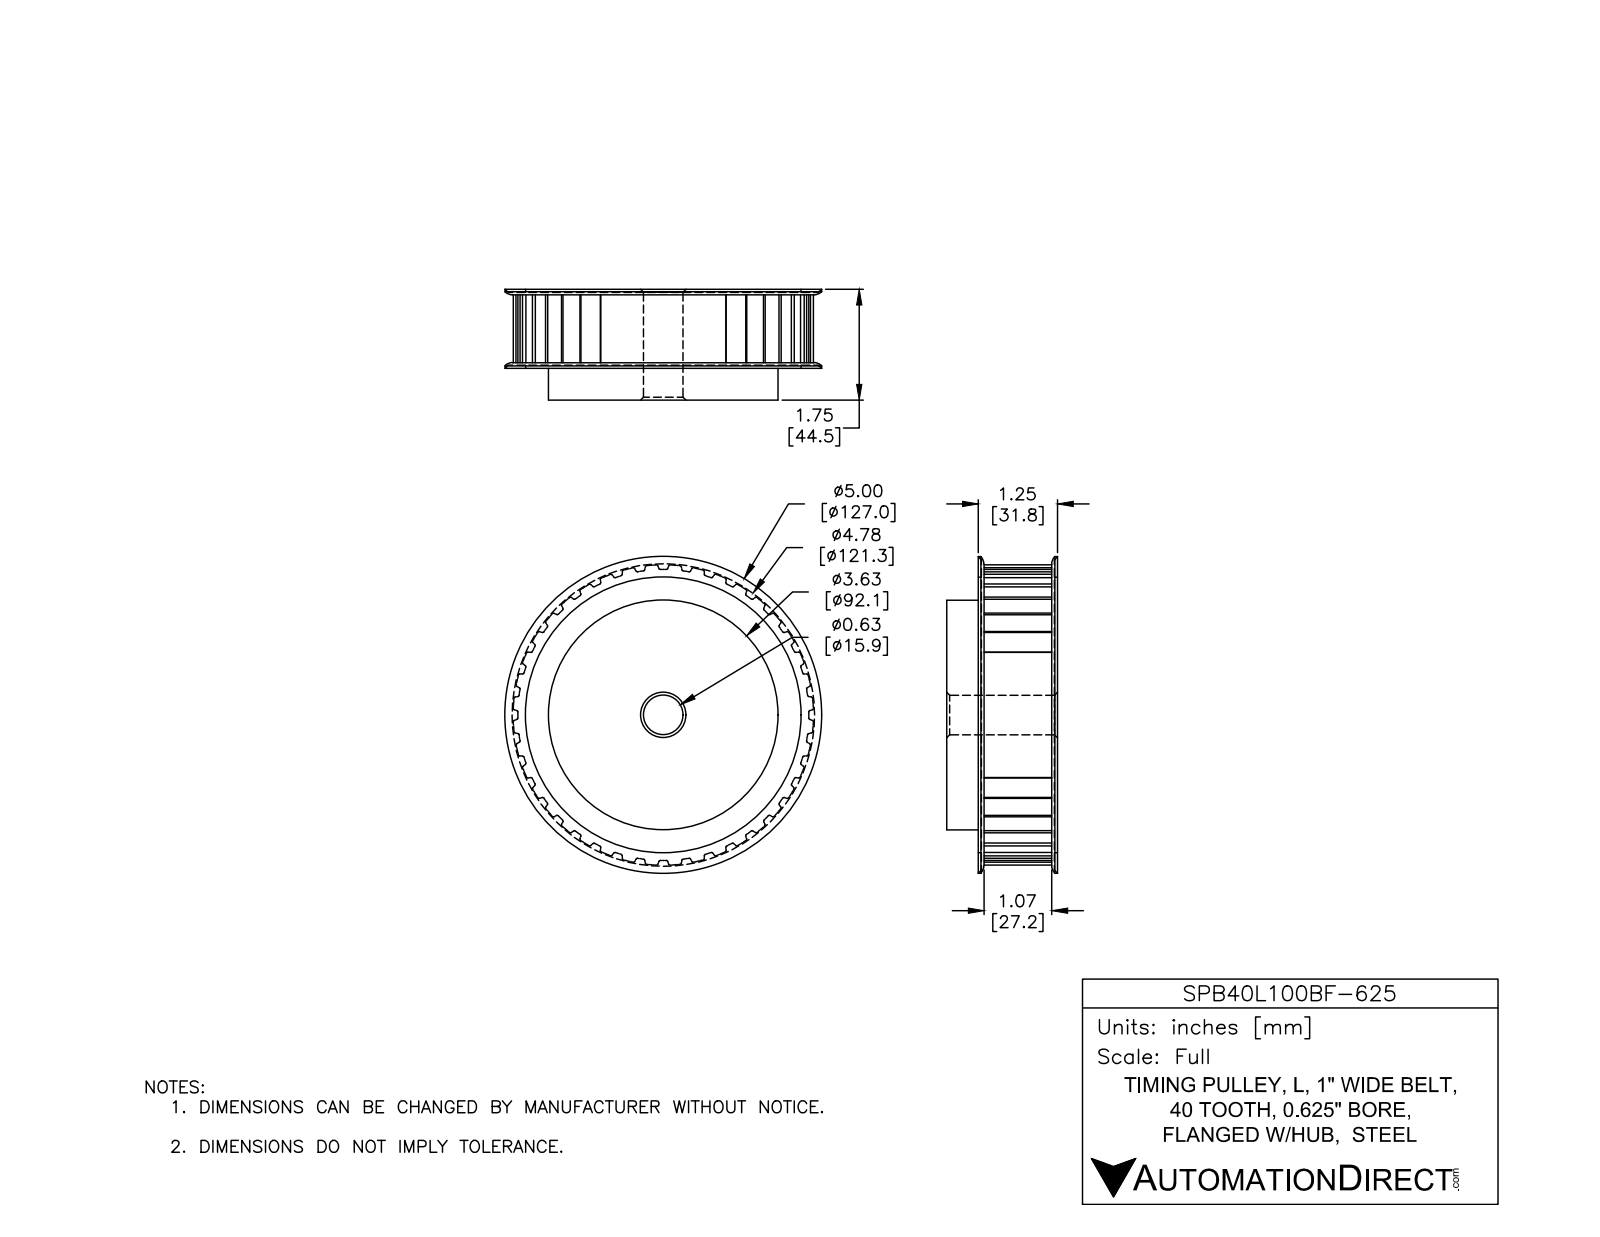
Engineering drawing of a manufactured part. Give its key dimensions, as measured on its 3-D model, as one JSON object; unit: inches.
{"part_name": "SPB40L100BF-625", "step_written_by": "SolidWorks 2015 (AUTOMOTIVE_DESIGN)", "units": "inches", "bodies": {"solids": 1, "faces": 385, "planar": 127, "cylindrical": 242, "other": 16}, "overall_size": [5, 5, 1.75], "volume_in3": 26.09, "surface_area_in2": 75.84, "round_holes": [[0.625, 1]], "round_bosses_or_shafts": [[5, 1], [4.35, 1], [3.625, 1]], "partial_cylinders_radius": [[0.02, 160], [2.372, 1], [2.373, 1]], "face_to_face_distances": [1.75, 0.05, 1.2, 1.25, 0.5, 1.7, 1.15, 0.55, 0.09, 1.16]}
